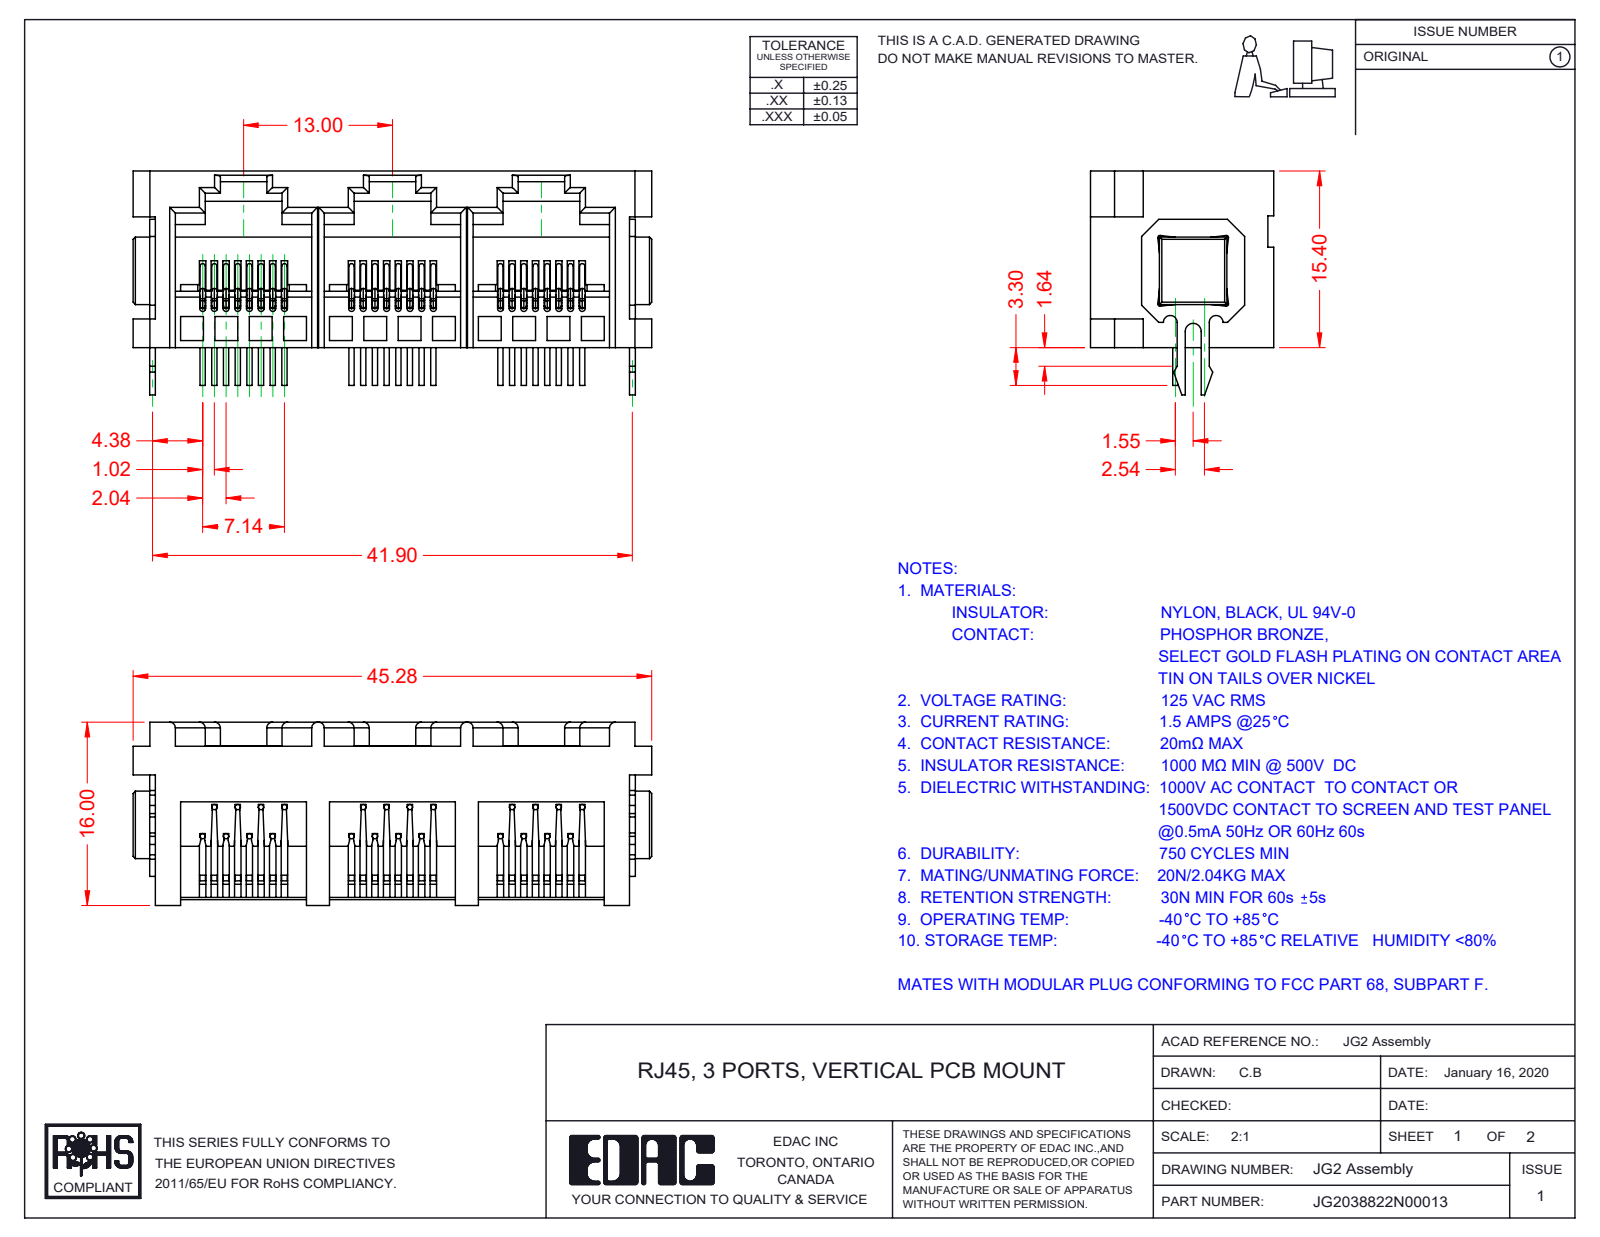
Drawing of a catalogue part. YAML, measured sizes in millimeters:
part_name: "G2 Boardlock1; G2 Insulator; G2 Boardlock2; G2 Contacts (+2 more)"
step_written_by: "SolidWorks 2016 (CONFIG_CONTROL_DESIGN)"
units: millimeters
bodies: {solids: 30, faces: 1835, planar: 1210, cylindrical: 457, other: 168}
overall_size: [45.28, 19.54, 16]
volume: 4876
surface_area: 9571
round_bosses_or_shafts:
  - {diameter: 0.46, count: 96}
partial_cylinders:
  - {radius: 0.5, count: 69}
  - {radius: 0.2, count: 4}
  - {radius: 20.35, count: 4}
  - {radius: 0.3, count: 3}
  - {radius: 0.6, count: 2}
  - {radius: 0.21, count: 1}
  - {radius: 0.45, count: 1}
  - {radius: 0.7, count: 1}
face_to_face_distances: [13, 12, 0.5, 3.4, 2.2, 11.08, 0.92, 26, 11, 2]
